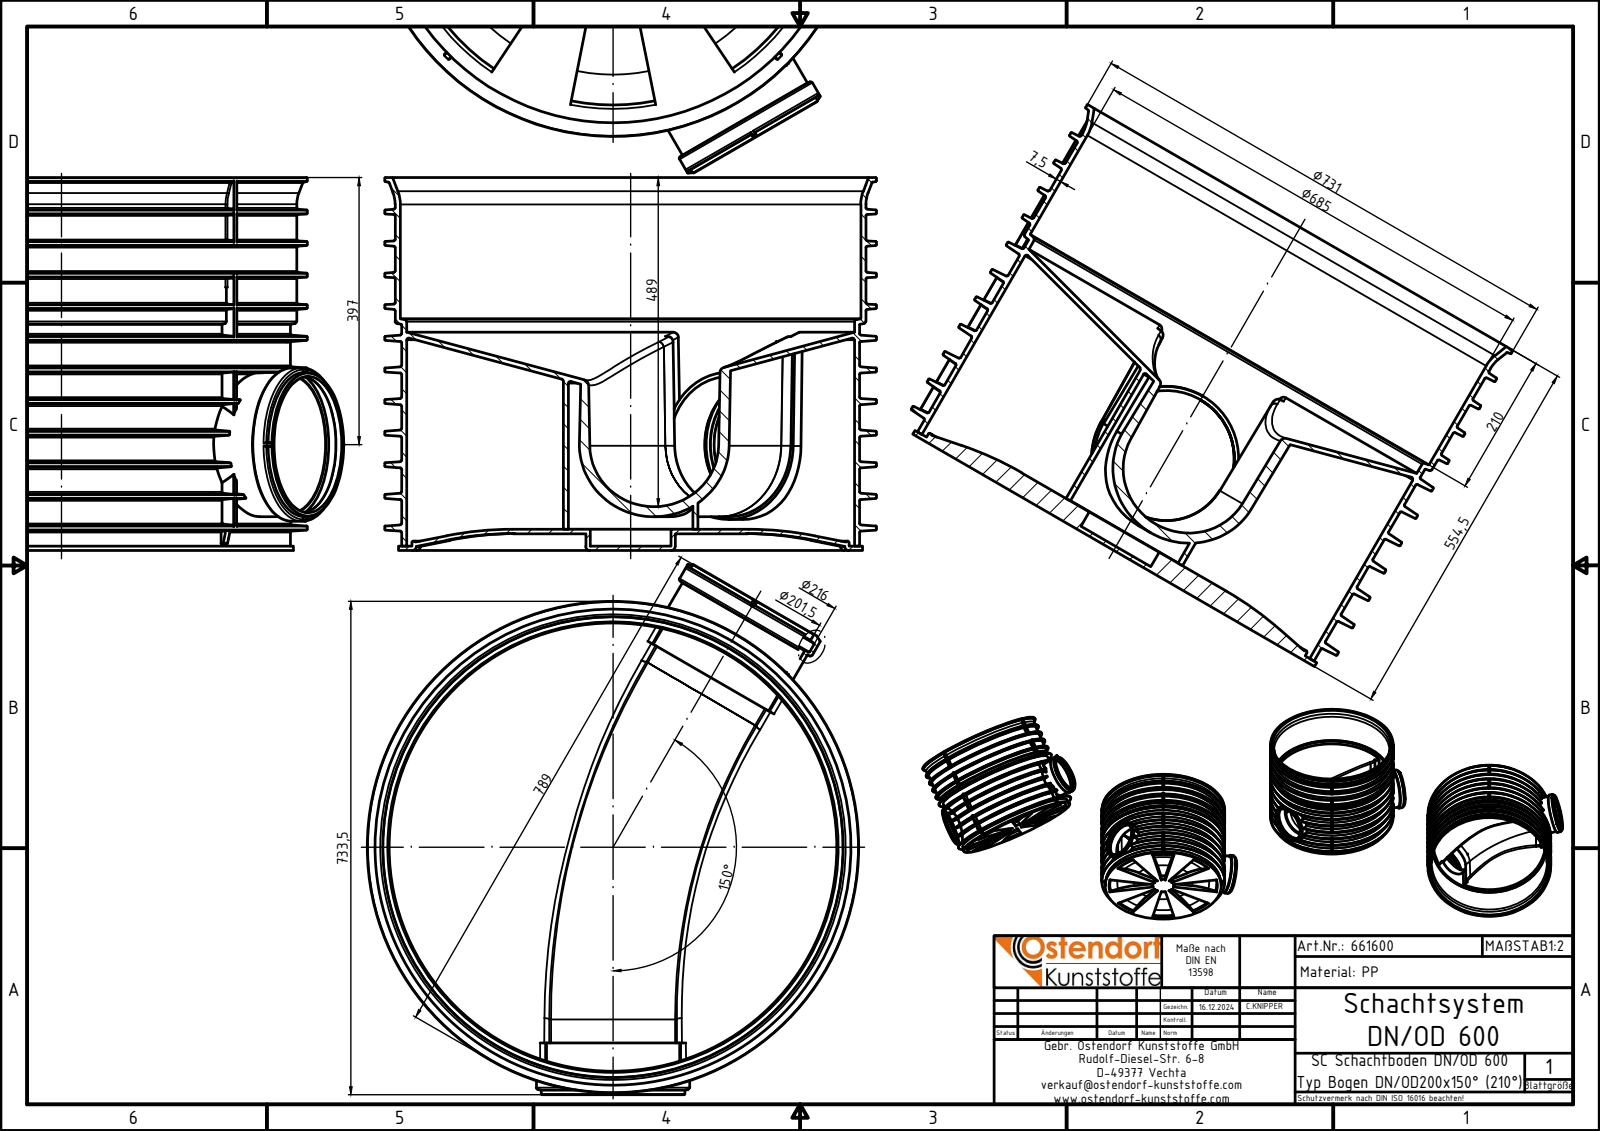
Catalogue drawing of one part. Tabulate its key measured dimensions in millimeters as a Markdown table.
| quantity | value |
| --- | --- |
| part name | 661600z; 661600 Schacht DN600 Boden; 661600 Schachtboden DN600 Grundkörper |
| STEP written by | Autodesk Inventor 2024 (AUTOMOTIVE_DESIGN) |
| units | millimeters |
| bodies | 2 solids, 1468 faces (201 planar, 219 cylindrical, 1048 other) |
| overall size | 787.93 × 731 × 554.5 |
| volume | 25 800 000 mm³ |
| surface area | 5 565 000 mm² |
| round holes (diameter × count) | 201.5 × 3, 216 × 2, 120 × 1, 185 × 1, 640 × 1, 666 × 1, 685 × 1 |
| round bosses / shafts (diameter × count) | 228 × 2, 214.5 × 2, 213.5 × 2, 731 × 1, 700 × 1, 690 × 1, 681 × 1, 650 × 1 |
| partial cylindrical surfaces (radius × count) | 1 × 36, 2 × 16, 92.35 × 3, 111.35 × 2, 66.5 × 1, 107.25 × 1, 318.5 × 1 |
| main face-to-face distances | 6.5, 25, 31.5, 18.5, 554.5, 548, 529.5, 523, 13, 7.5 |
